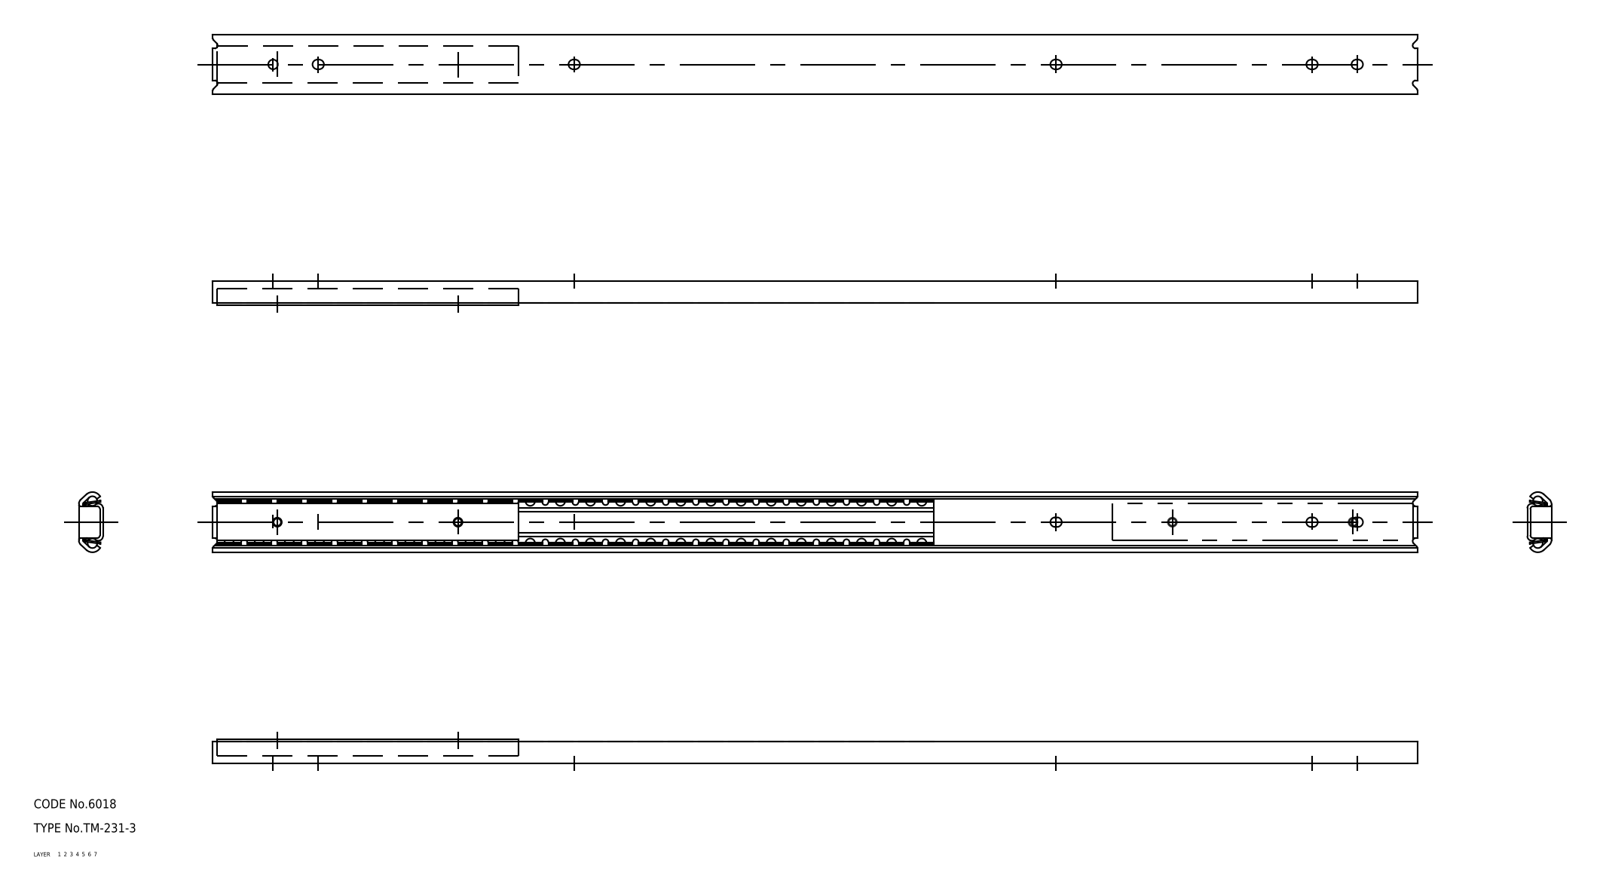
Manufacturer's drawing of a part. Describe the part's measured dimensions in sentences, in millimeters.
The part is named "ball; retainer; member_B; member_A (+1 more)". Its 3-D file was written by "CADfix (AUTOMOTIVE_DESIGN)". It is 51 solids with 630 faces: 0 planar, 0 cylindrical and 630 other. Overall it measures 400 by 20 by 8 millimeters. Its volume is 21 238 cubic millimeters and its surface area 40 307 square millimeters.
